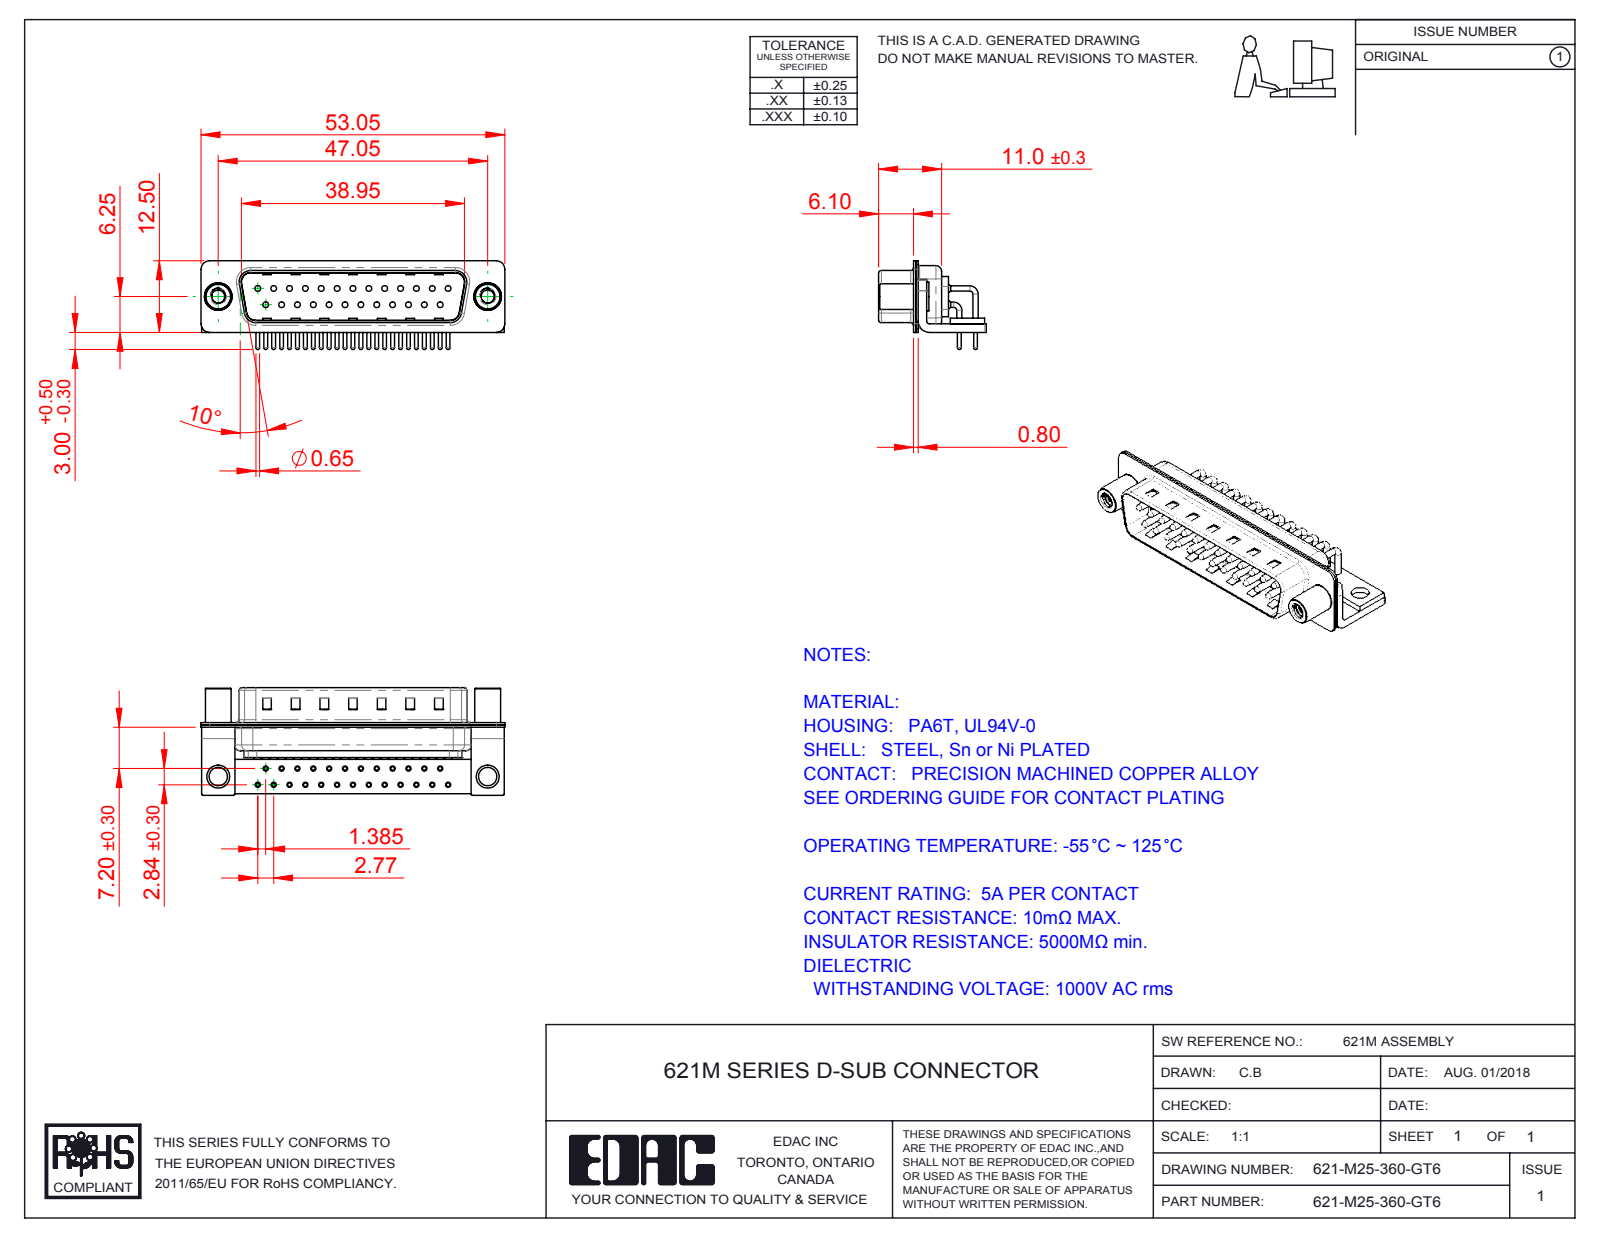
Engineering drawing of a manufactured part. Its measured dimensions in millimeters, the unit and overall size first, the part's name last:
Units: millimetres
Overall size (bounding box): 53.05 × 18.8 × 15.49
Round holes (diameter × count): ⌀0.9 ×25, ⌀1 ×25, ⌀1.7 ×25, ⌀2 ×25, ⌀2.26 ×2, ⌀3.2 ×2, ⌀4 ×2, ⌀4.8 ×2
Round bosses / shafts (diameter × count): ⌀0.9 ×33, ⌀1.5 ×25, ⌀0.65 ×25, ⌀5 ×2, ⌀4.9 ×2, ⌀4.5 ×2
Partial cylindrical surfaces — rounded edges, fillets, slot ends (radius × count): R1.01 ×25, R0.25 ×16, R1.5 ×16, R2 ×13, R0.5 ×9, R1.6 ×8, R0.6 ×4, R0.65 ×4
Main face-to-face distances: 0.4, 0.85, 1.25, 1.5, 9.55, 0.8, 10.4, 8.3, 1, 1.9
Hole centre spacings: 3.16, 2.77, 8.31, 5.54, 11.08, 13.85, 5.04, 16.62
Volume: 3 511 mm³ · Surface area: 9 207 mm²
Bodies: 33 solids, 3276 faces (1799 planar, 1151 cylindrical, 326 other)
Part name (STEP PRODUCT): 621M Housing_25 Contacts; 621M Contact Row 1; 621M Stabilizer Board_25 Contacts; 621M Shell Front_25 Contacts (+5 more)
STEP written by: SolidWorks 2016 (CONFIG_CONTROL_DESIGN)
